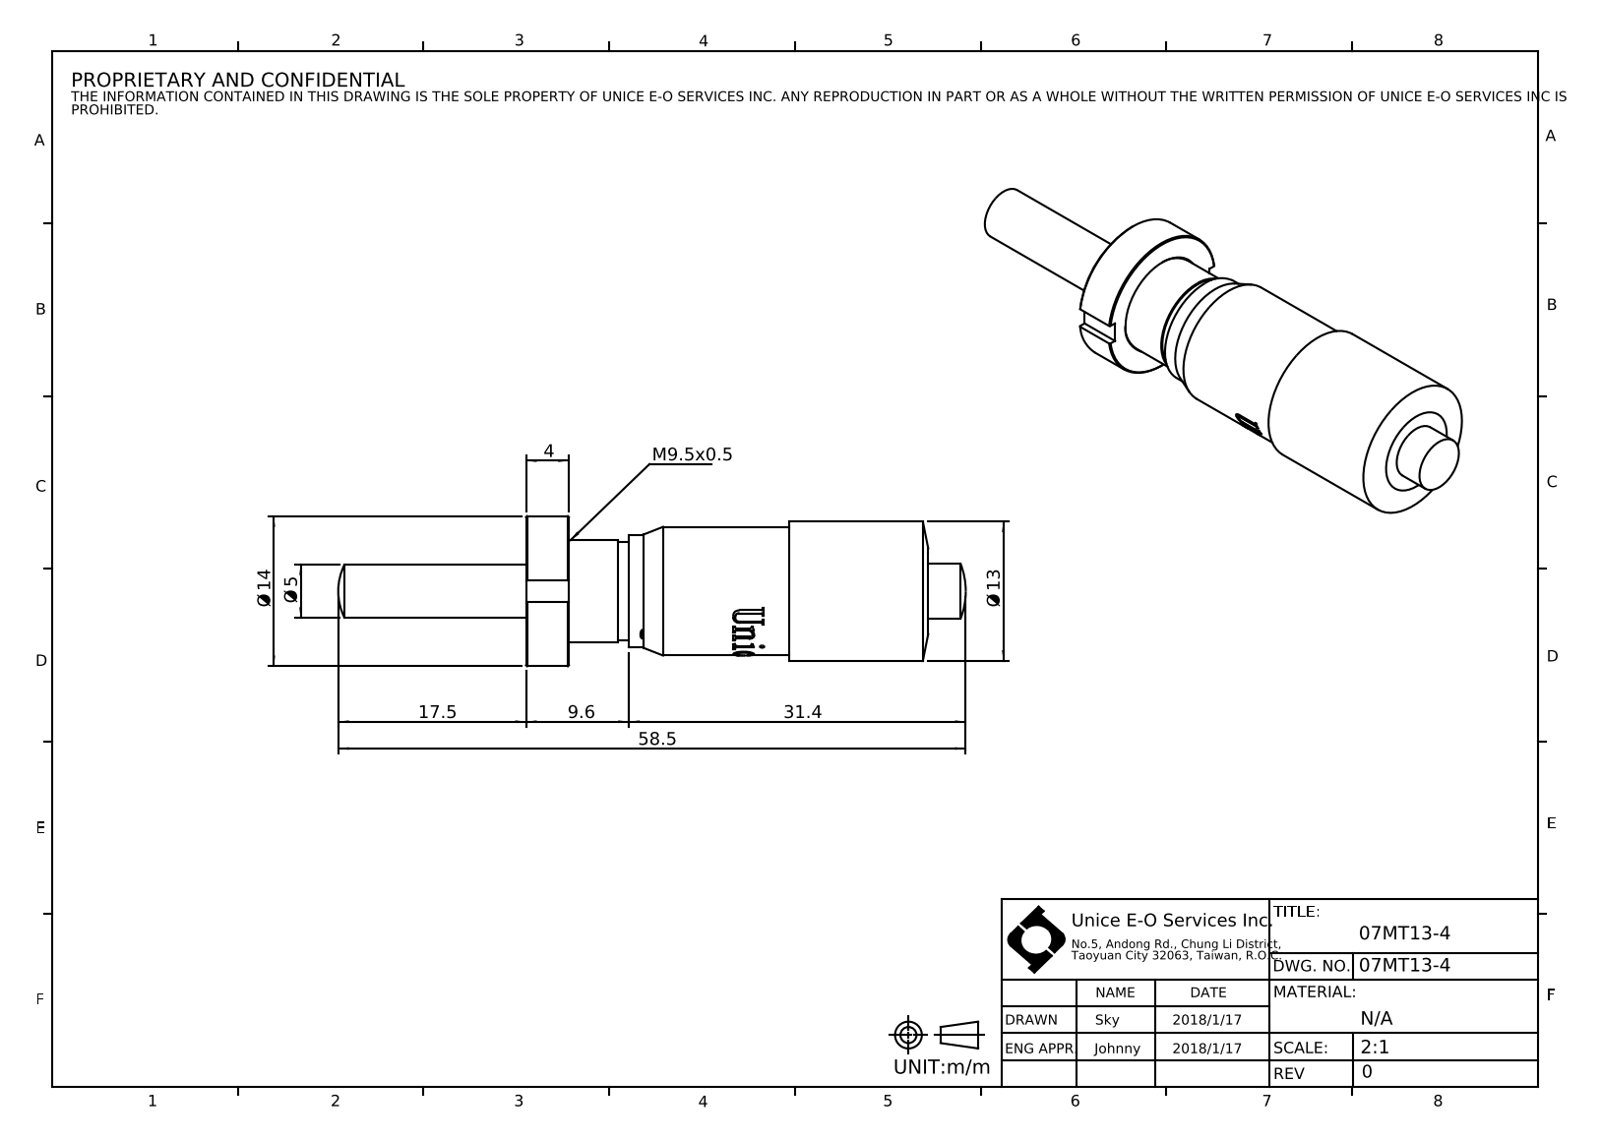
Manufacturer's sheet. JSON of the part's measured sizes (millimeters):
{"part_name": "07MT13-4", "step_written_by": "SolidWorks 2016 (AUTOMOTIVE_DESIGN)", "units": "millimeters", "bodies": {"solids": 0, "faces": 106, "planar": 27, "cylindrical": 32, "other": 47}, "overall_size": [58.5, 14, 13.86], "round_holes": [[9.5, 1], [10.6, 1]], "round_bosses_or_shafts": [[14, 1], [13, 1], [12, 1], [10.5, 1], [9.2, 1], [5.2, 1], [5, 1]], "partial_cylinders_radius": [[5.98, 1]], "face_to_face_distances": [4, 37.5, 33.5, 9.6, 5.6, 27.9, 24.5, 20.5, 14.9, 13]}
